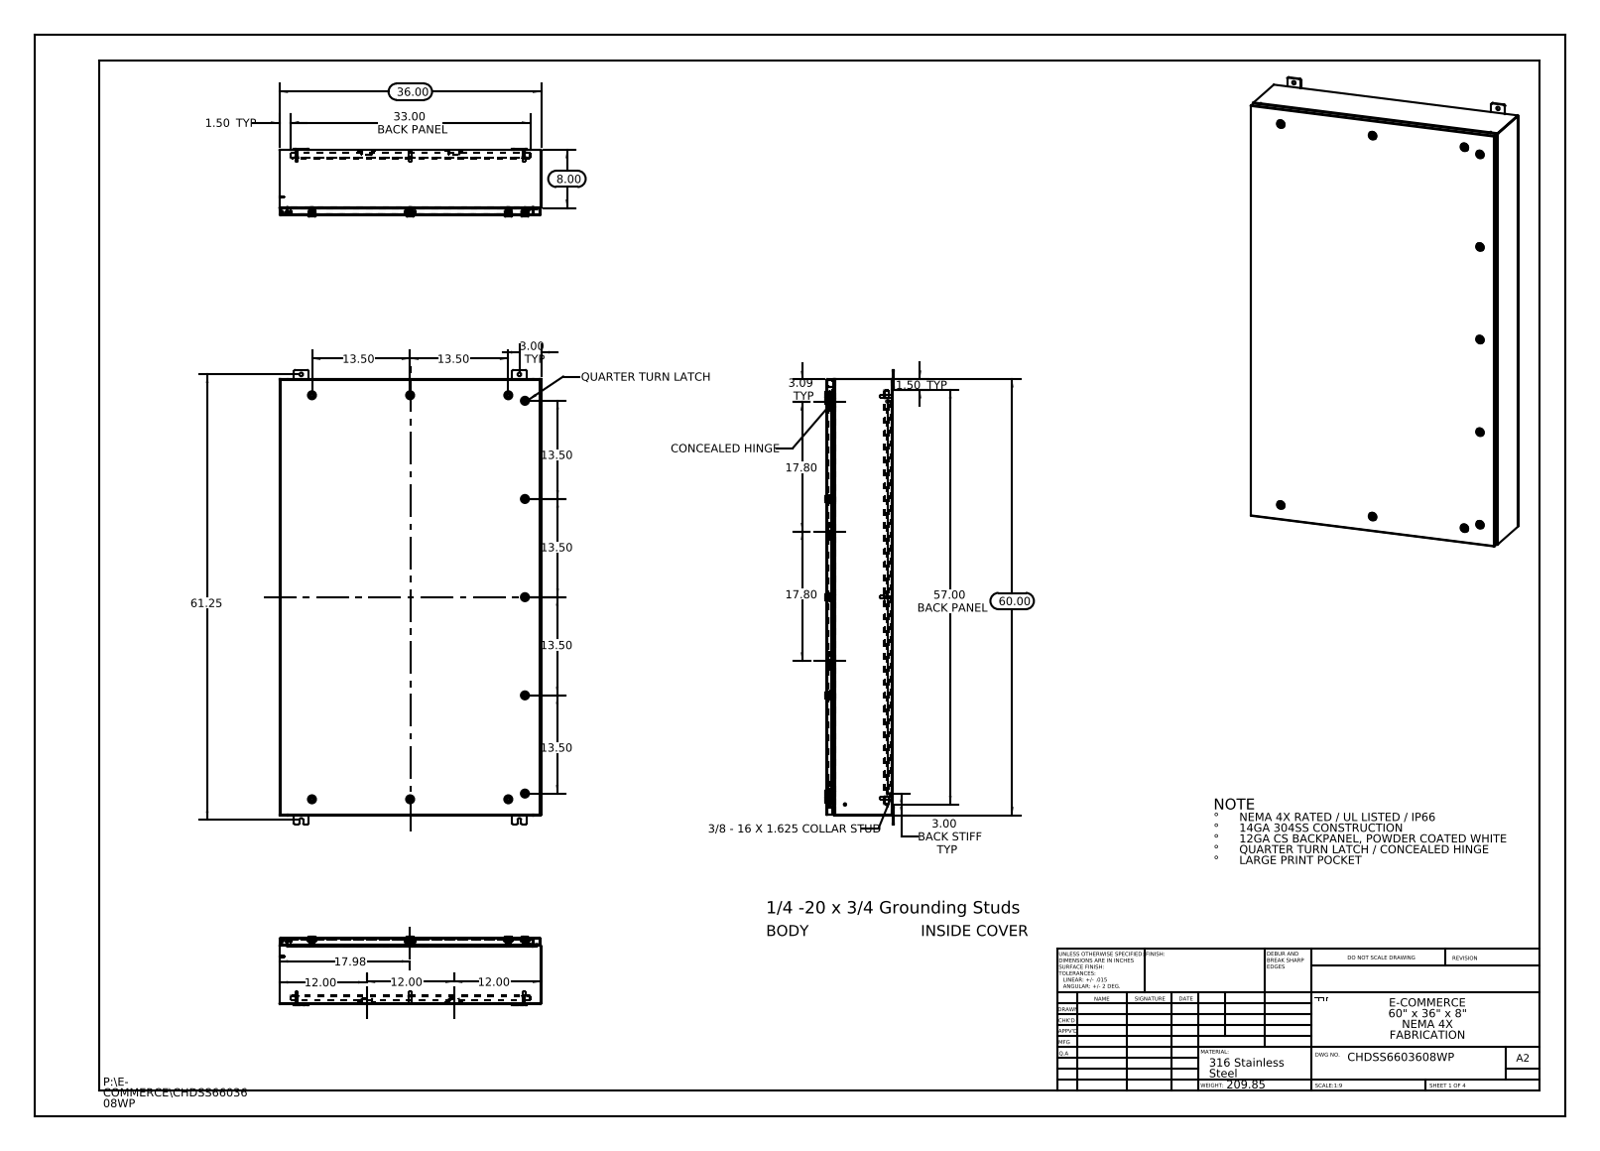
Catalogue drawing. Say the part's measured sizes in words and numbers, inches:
The part is named "Washer-221320-IB-Industrilas_Washer-221320-IB-Industrilas; Concealed Hinge enclosure side; CHDSS6603608WP Mounting Studs; CHDSS6603608WP Top (+8 more)". Its 3-D file was written by "SolidWorks 2013 (CONFIG_CONTROL_DESIGN)". It is 103 solids with 9942 faces: 2871 planar, 3101 cylindrical and 3970 other. Overall it measures 62.5 by 36 by 9.356 inches. Its volume is 740 cubic inches and its surface area 18 260 square inches. Round holes: 11 of diameter 0.197, 11 of diameter 0.394, 11 of diameter 0.4, 11 of diameter 0.5, 11 of diameter 0.63, 11 of diameter 0.787, 8 of diameter 0.136, 8 of diameter 0.25, 1 of diameter 0.211. Round bosses or shafts: 13 of diameter 0.236, 11 of diameter 1.102, 11 of diameter 0.78, 11 of diameter 0.626, 11 of diameter 0.61, 11 of diameter 0.531, 11 of diameter 0.392, 11 of diameter 0.114. Partial cylindrical surfaces (rounded edges, fillets, slot ends): 363 of radius 0.006, 363 of radius 0.118, 132 of radius 0.028, 44 of radius 0.02, 44 of radius 0.197, 34 of radius 0.013, 30 of radius 0.088, 22 of radius 0.039. The main face-to-face distances are 0.075, 0.074, 8.861, 8.936, 9.01, 8.935, 0.104, 1, 1.075, 7.861. The hole center spacings are 13.5, 17.796, 27, 0.688, 2.224, 27.625, 35.591, 41.709.
